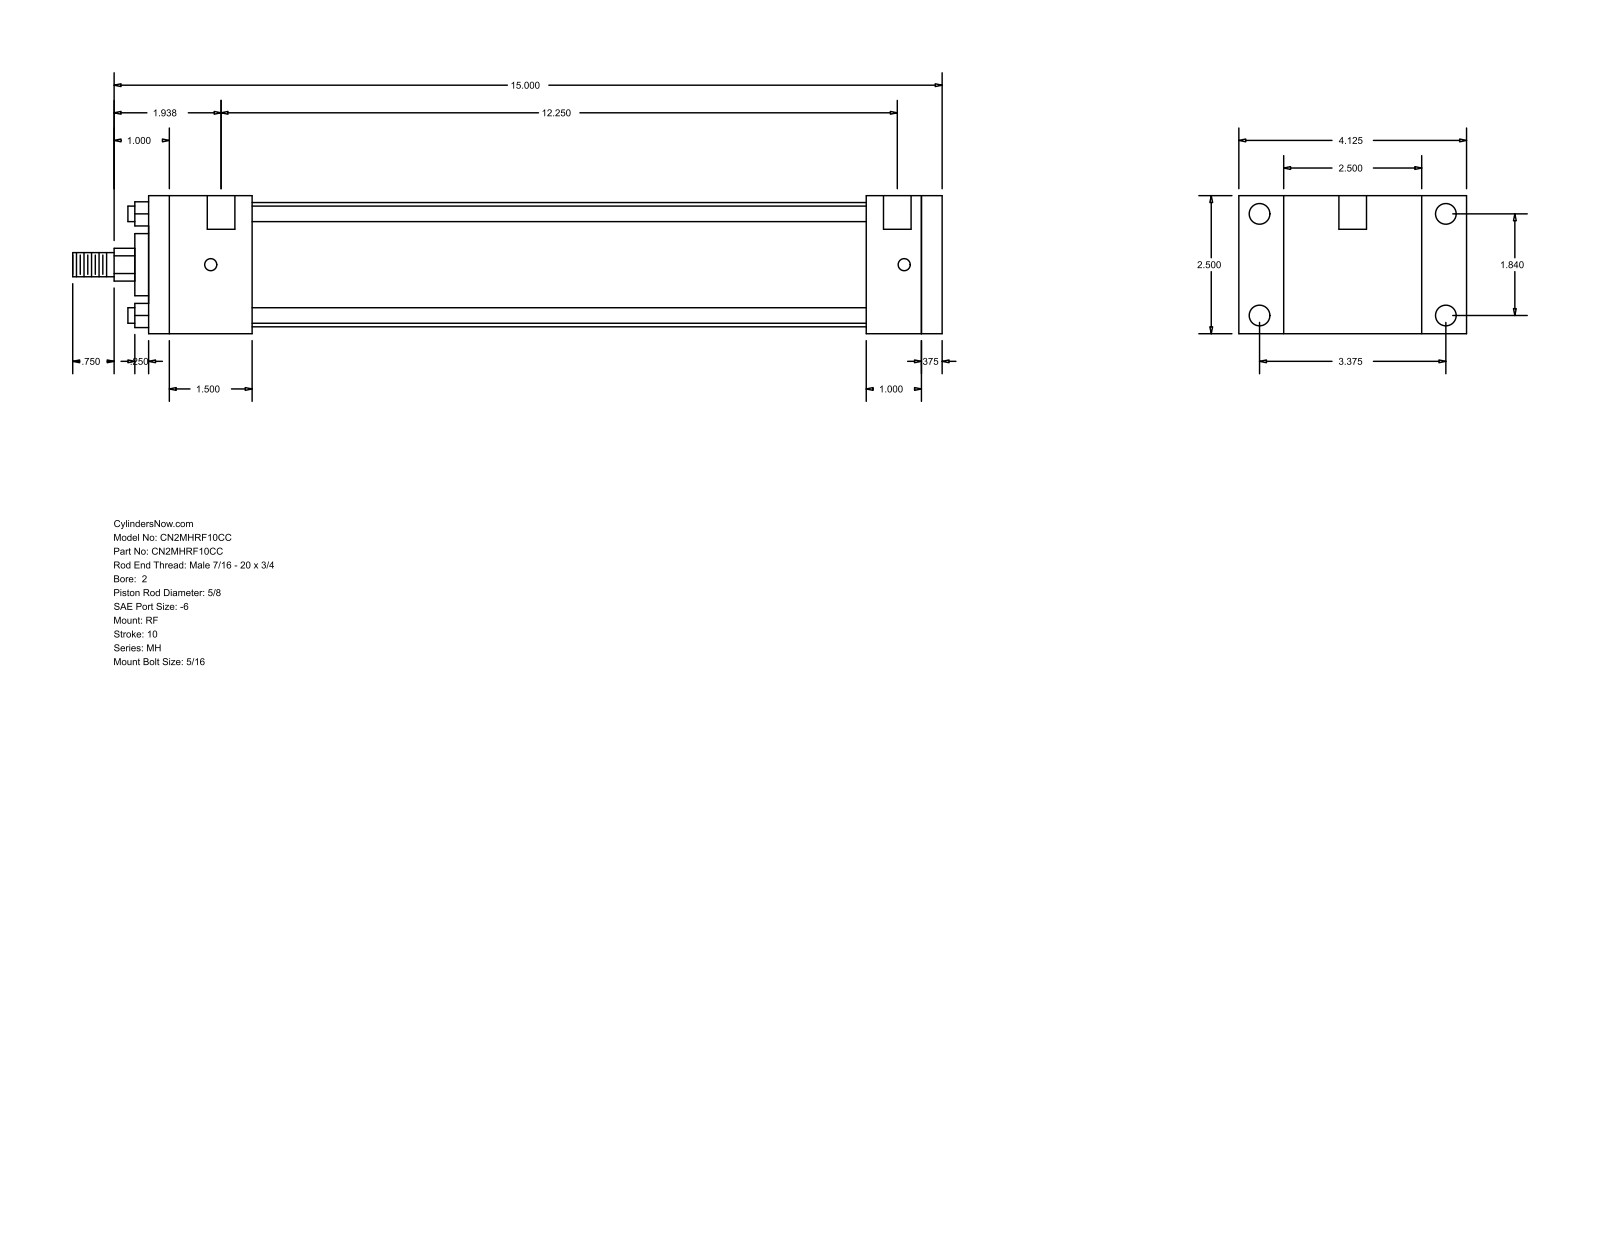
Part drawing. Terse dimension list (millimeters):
name: MH_RF__0200_0.625
written by: GSSL Pune (CONFIG_CONTROL_DESIGN)
unit: mm
bodies: 0 solids, 92 faces (64 planar, 28 cylindrical, 0 other)
size: 400.05 × 104.78 × 63.5
holes: 4× ⌀5.56, 4× ⌀9.53, 2× ⌀12.7
bosses: 4× ⌀7.14, 1× ⌀57.15, 1× ⌀28.57, 1× ⌀15.88, 1× ⌀11.11
rounds: 1× R7.54
face distances: 63.5, 365.12, 355.6, 9.52, 34.93, 47.62, 330.19, 282.57, 307.98, 317.5
hole spacings: 46.74, 85.72, 97.63, 319.09, 3.18, 4.76, 311.15, 314.33
